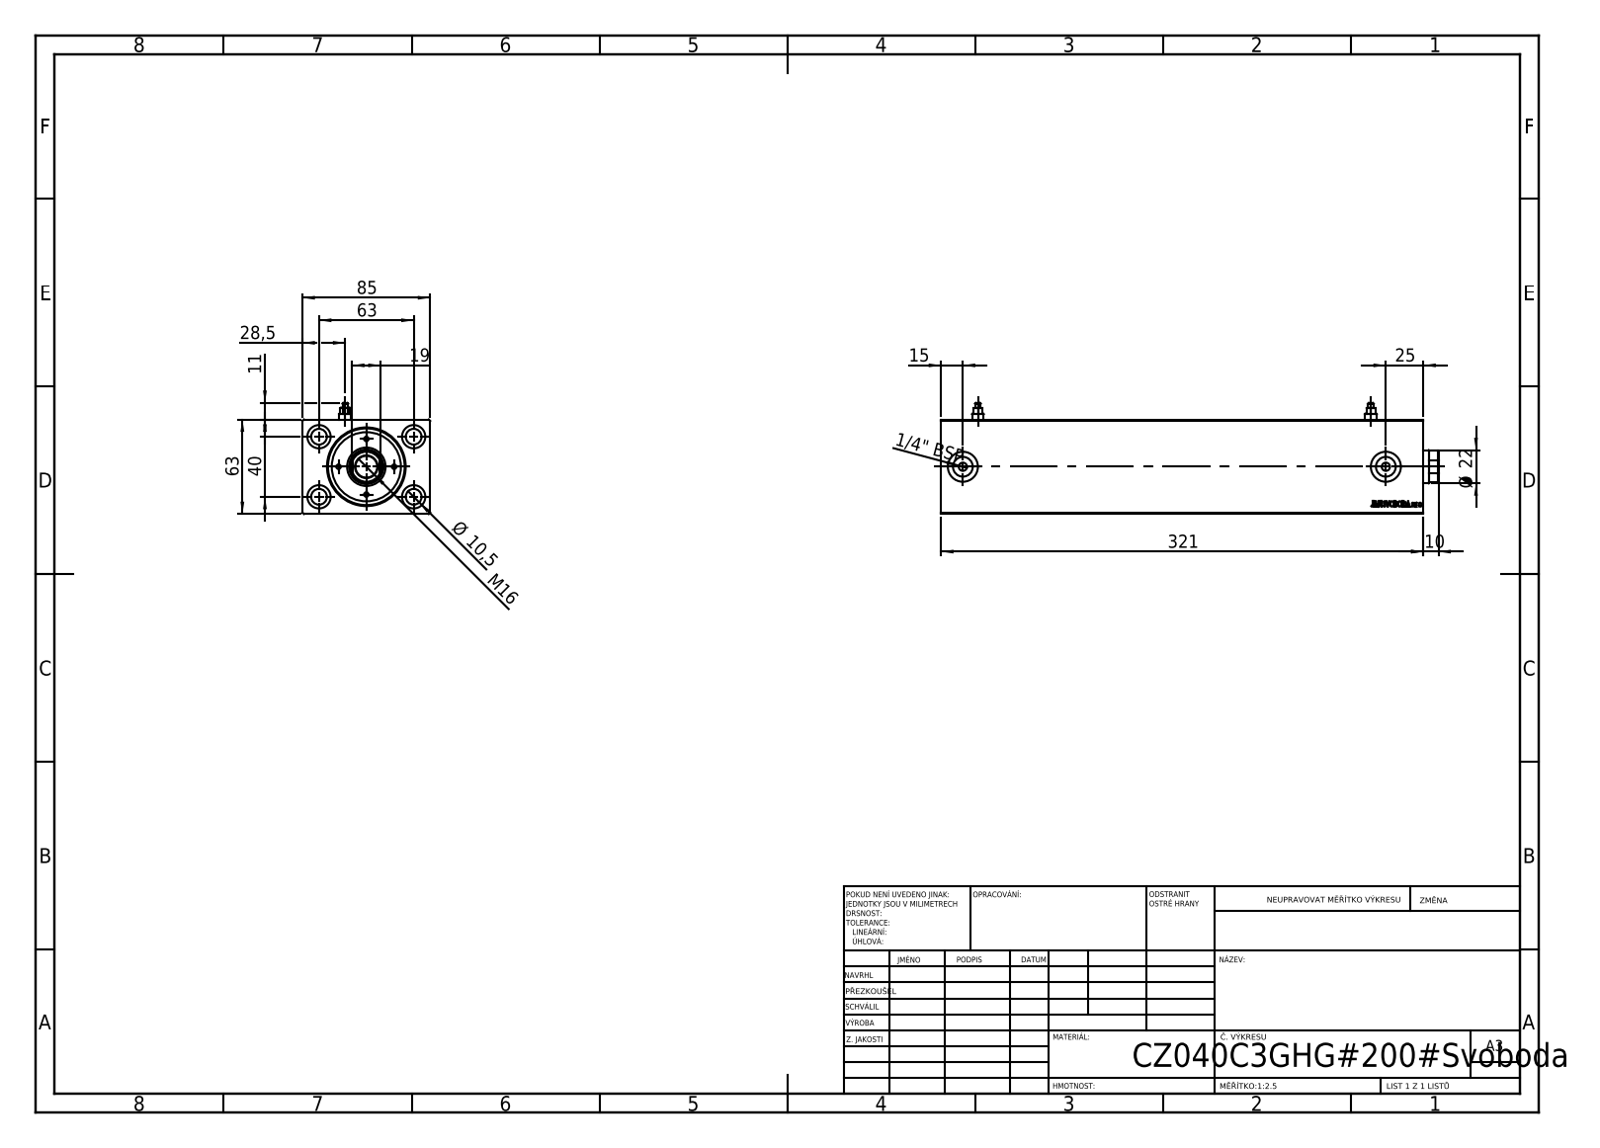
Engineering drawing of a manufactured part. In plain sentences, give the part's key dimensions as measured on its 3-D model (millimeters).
Its 3-D file was written by "SolidWorks 2019 (CONFIG_CONTROL_DESIGN)". It is 1 solid with 825 faces: 397 planar, 46 cylindrical and 382 other. Overall it measures 321 by 85 by 63 millimeters. Its volume is 1 202 000 cubic millimeters and its surface area 188 220 square millimeters. Round holes: 4 of diameter 10.5, 4 of diameter 15.5, 2 of diameter 5.5, 2 of diameter 8, 2 of diameter 13.16, 2 of diameter 20, 1 of diameter 36, 1 of diameter 40, 1 of diameter 51. The main face-to-face distances are 63, 85, 321, 305.7, 15.3, 320.8, 15.1, 103.22, 10.33, 310.67. The hole center spacings are 37.31, 40, 63, 74.63, 261.5, 281.5.
